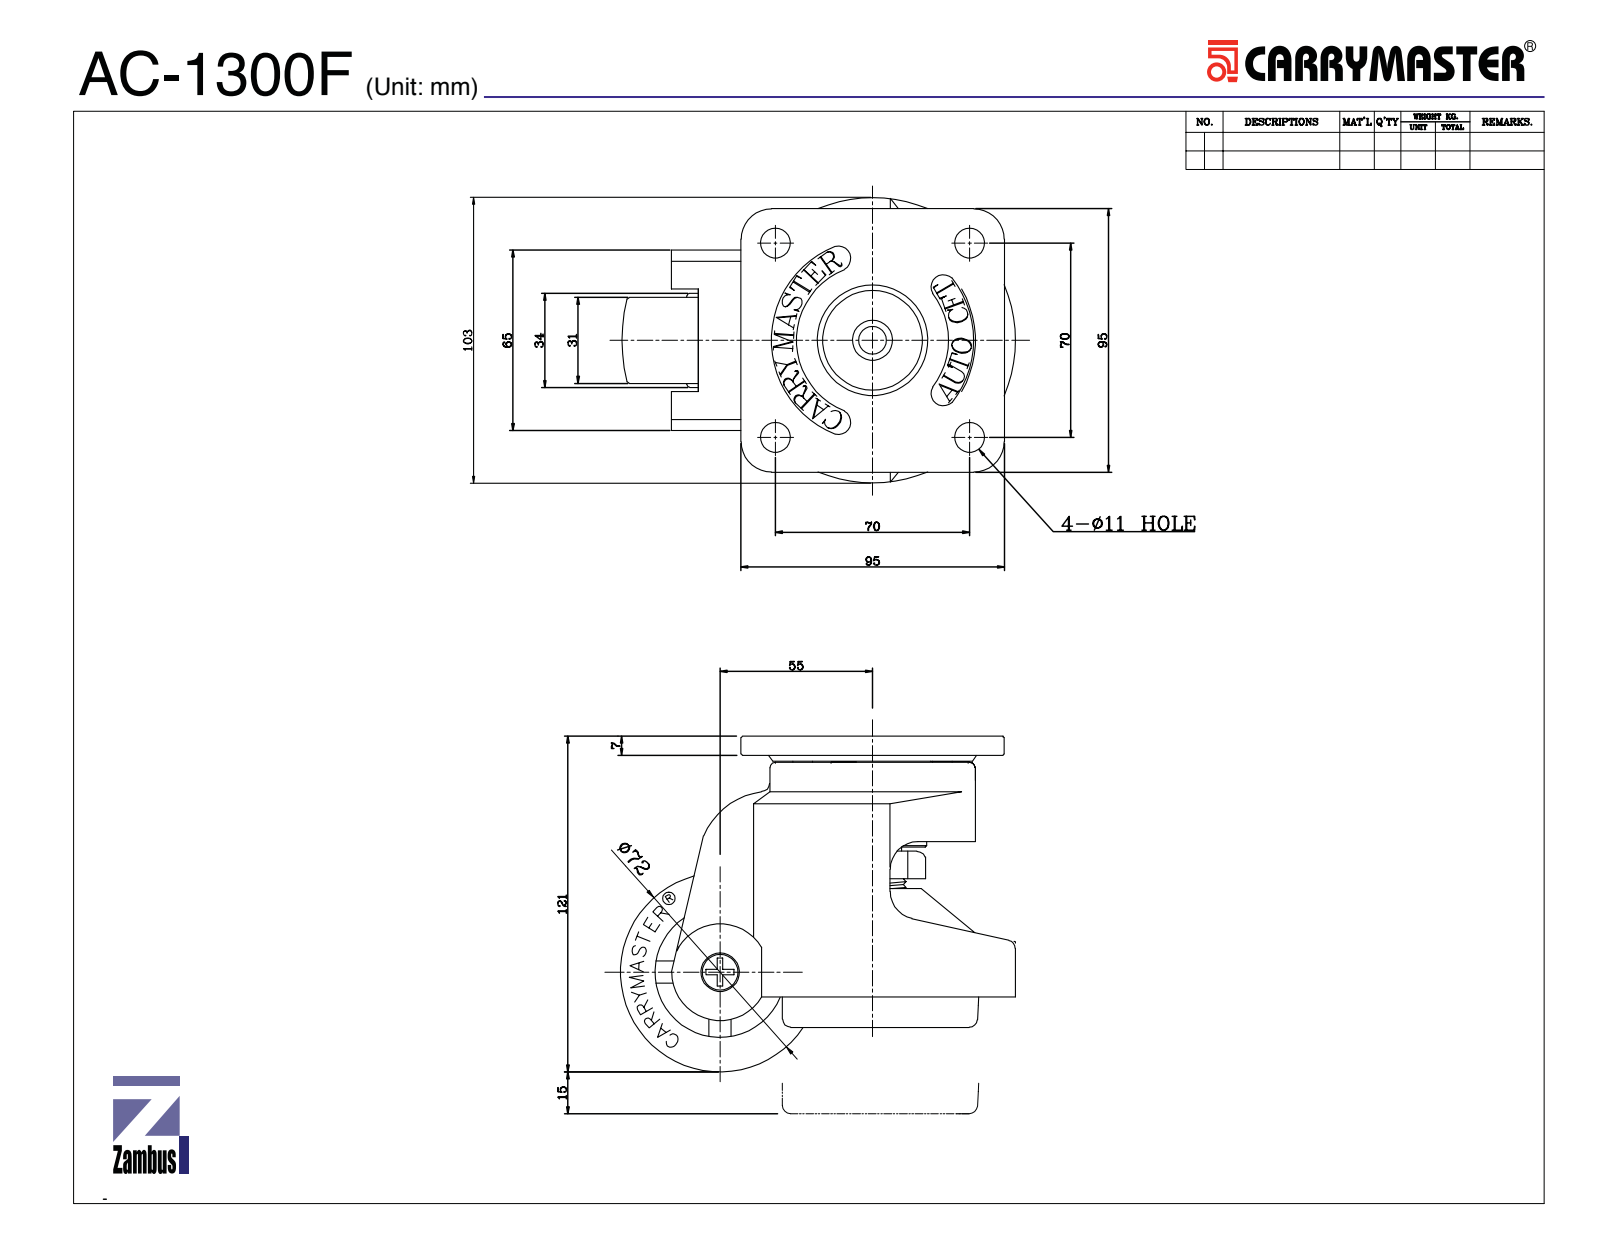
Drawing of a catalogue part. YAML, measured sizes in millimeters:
part_name: "AC-1300F"
step_written_by: "SolidWorks 2015 (CONFIG_CONTROL_DESIGN)"
units: millimeters
bodies: {solids: 32, faces: 2540, planar: 1920, cylindrical: 253, other: 367}
overall_size: [142.5, 121.39, 104.4]
volume: 603069
surface_area: 150967
round_holes:
  - {diameter: 11, count: 4}
  - {diameter: 6.8, count: 2}
  - {diameter: 1.63, count: 1}
  - {diameter: 9.7, count: 1}
  - {diameter: 12.2, count: 1}
  - {diameter: 13, count: 1}
  - {diameter: 13.5, count: 1}
  - {diameter: 14, count: 1}
  - {diameter: 17.5, count: 1}
  - {diameter: 22, count: 1}
  - {diameter: 30, count: 1}
  - {diameter: 40, count: 1}
round_bosses_or_shafts:
  - {diameter: 25, count: 2}
  - {diameter: 16, count: 2}
  - {diameter: 103, count: 1}
  - {diameter: 74, count: 1}
  - {diameter: 41.2, count: 1}
  - {diameter: 39, count: 1}
  - {diameter: 35, count: 1}
  - {diameter: 25.4, count: 1}
partial_cylinders:
  - {radius: 5, count: 20}
  - {radius: 8, count: 8}
  - {radius: 3, count: 6}
  - {radius: 2, count: 4}
  - {radius: 11, count: 4}
  - {radius: 10, count: 2}
  - {radius: 1.49, count: 1}
  - {radius: 2.08, count: 1}
face_to_face_distances: [6, 50, 32.39, 35.5, 2.5, 38.39, 56, 24.5, 8, 33.5]
hole_center_spacings: [49.5, 70, 98.99, 26.29]
